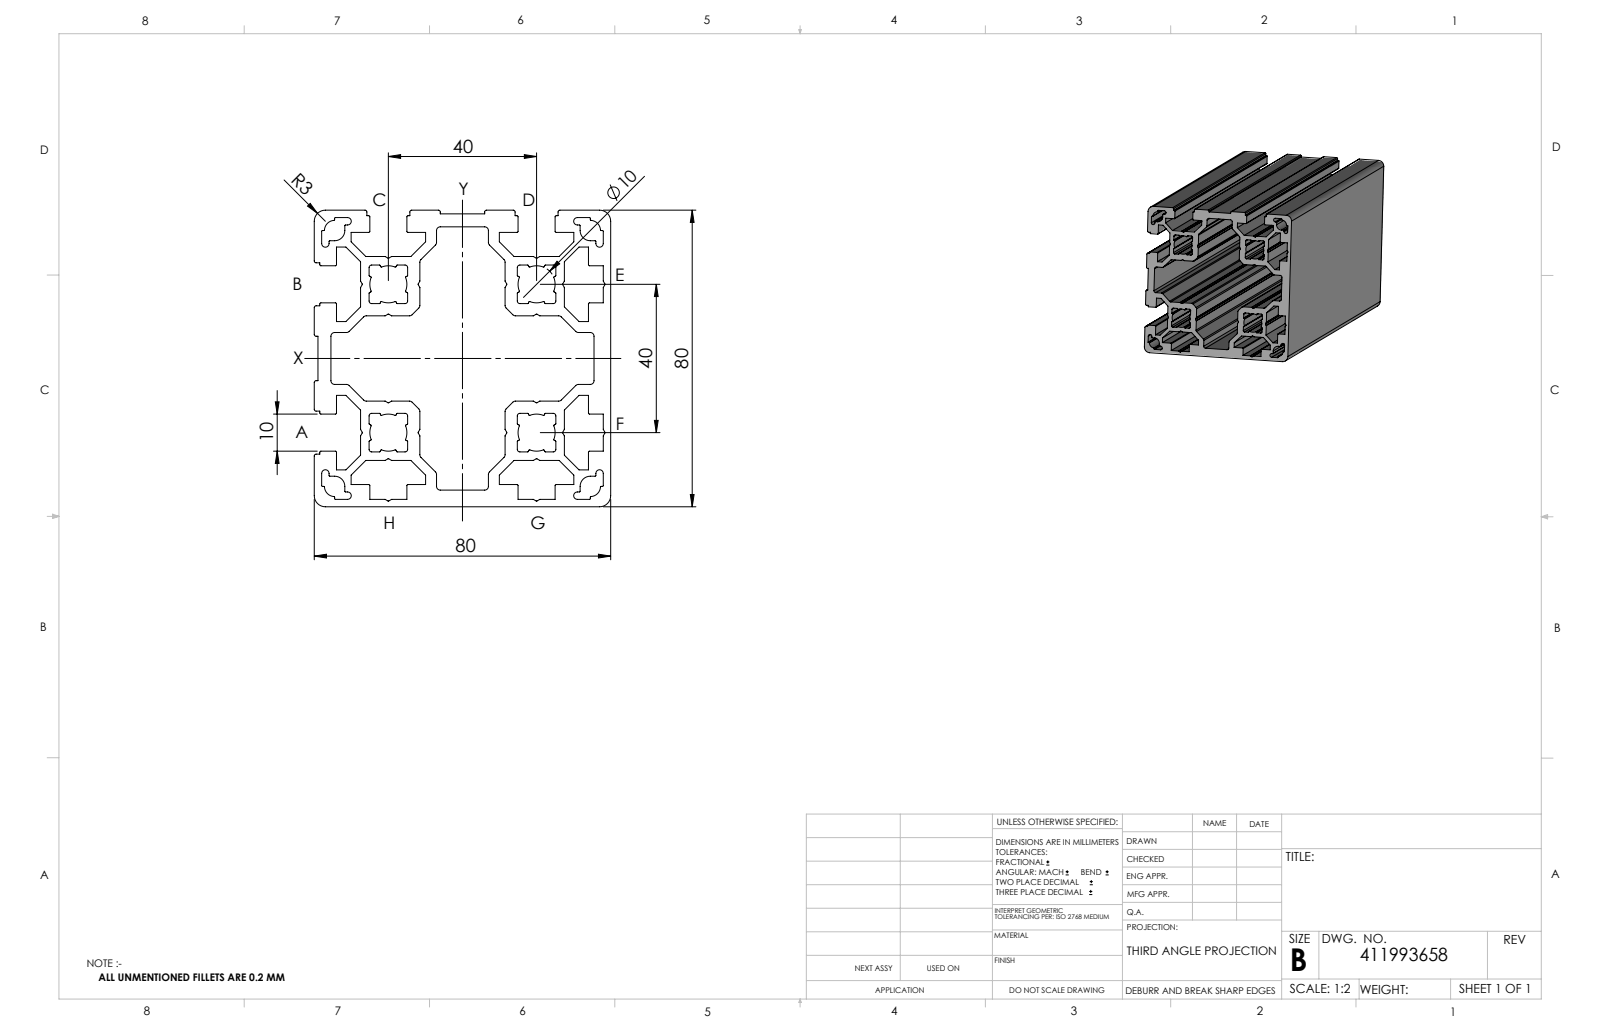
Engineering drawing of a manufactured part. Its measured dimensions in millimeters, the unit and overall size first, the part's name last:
Units: millimetres
Overall size (bounding box): 200 × 80 × 80
Partial cylindrical surfaces — rounded edges, fillets, slot ends (radius × count): R0.2 ×148, R1 ×40, R0.3 ×24, R0.7 ×16, R0.5 ×12, R2.75 ×4, R3 ×4, R5 ×4
Main face-to-face distances: 12.5, 2.5, 16, 67.5, 28.5, 51.5, 39, 6, 74, 6.5
Volume: 394 788 mm³ · Surface area: 252 305 mm²
Bodies: 1 solid, 584 faces (298 planar, 286 cylindrical, 0 other)
Part name (STEP PRODUCT): 411993658_c_1
STEP written by: SolidWorks 2014 (CONFIG_CONTROL_DESIGN)
